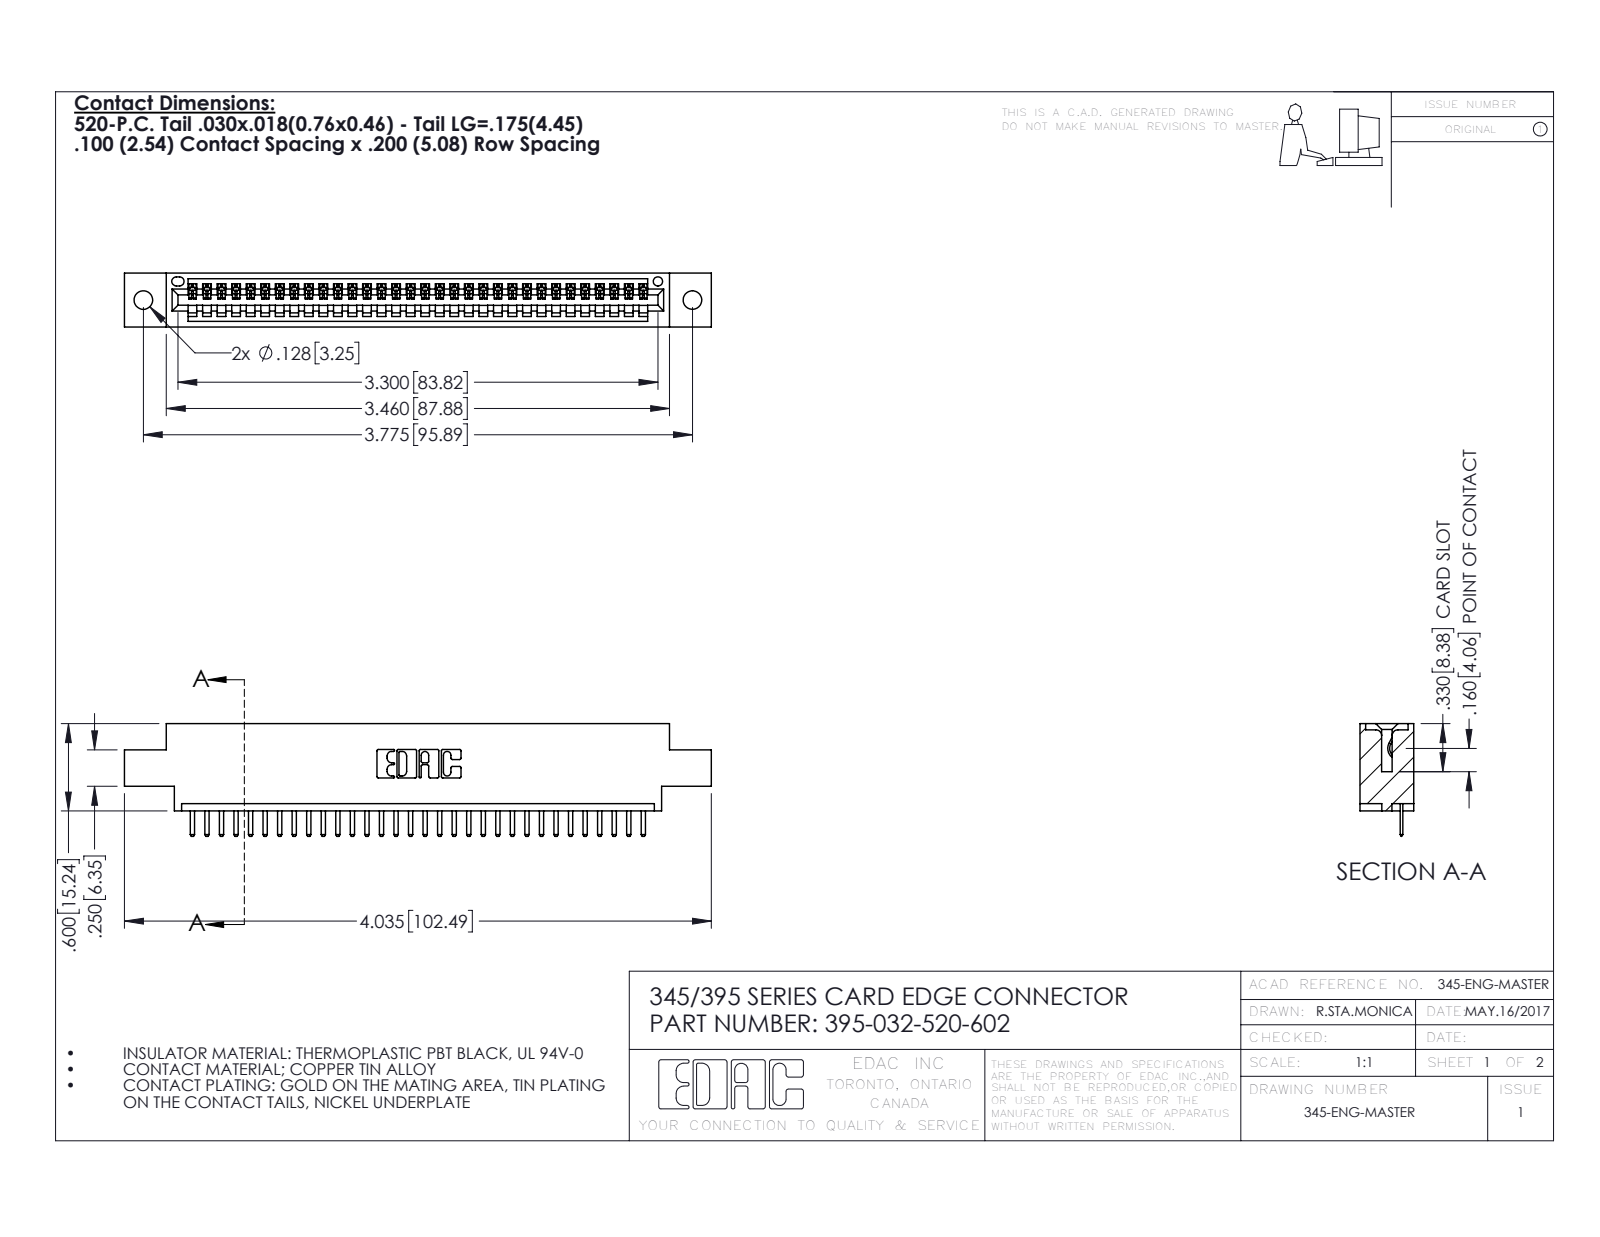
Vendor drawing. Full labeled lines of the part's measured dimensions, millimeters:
Part name (STEP PRODUCT): 345-292-001_345-293-120; 345 Part_0.170 Offset - 0.128 Dia; 395-032-520-602
STEP written by: SolidWorks 2016 (CONFIG_CONTROL_DESIGN)
Units: millimetres
Bodies: 33 solids, 2114 faces (1428 planar, 686 cylindrical, 0 other)
Overall size (bounding box): 102.5 × 19.7 × 9.4
Volume: 9 410 mm³ · Surface area: 11 920 mm²
Round holes (diameter × count): ⌀3.3 ×2, ⌀1.6 ×1
Partial cylindrical surfaces — rounded edges, fillets, slot ends (radius × count): R0.3 ×66, R0.2 ×64, R0.3 ×22, R0.2 ×6, R0.8 ×6, R0.7 ×3, R0.8 ×2, R1 ×2
Main face-to-face distances: 7.6, 1.8, 9.4, 5.1, 2.5, 6.9, 0.6, 5.7, 1.8, 4.4
Hole centre spacings: 6.9, 89.9, 95.9
